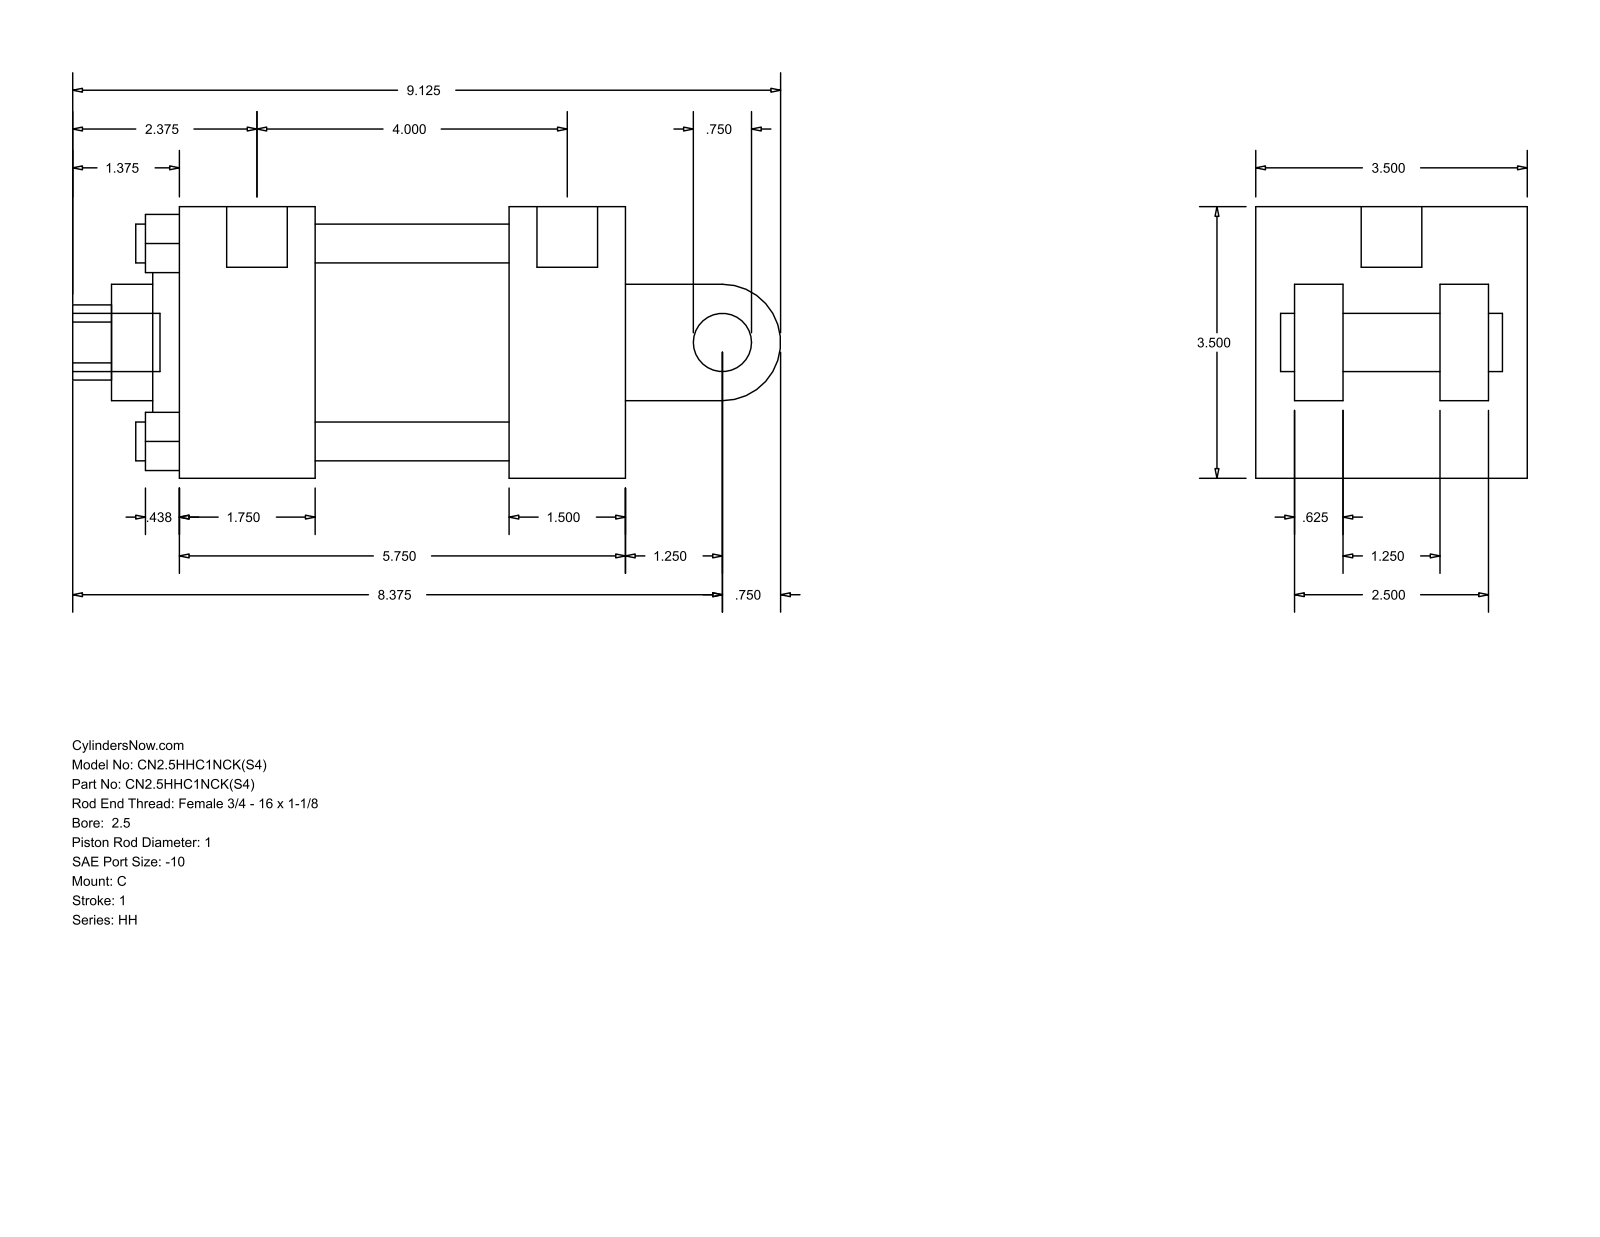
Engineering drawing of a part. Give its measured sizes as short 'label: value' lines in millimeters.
name: HH_C__0250_1
written by: GSSL Pune (CONFIG_CONTROL_DESIGN)
unit: mm
bodies: 0 solids, 101 faces (71 planar, 30 cylindrical, 0 other)
size: 231.78 × 88.9 × 88.9
holes: 4× ⌀12.7, 2× ⌀5.56, 1× ⌀19.84, 1× ⌀25.4, 1× ⌀38.1, 1× ⌀60.33, 1× ⌀73.03
bosses: 2× ⌀19.05, 2× ⌀5.56, 1× ⌀19.84
rounds: 1× R12.29, 1× R19.05
face distances: 88.9, 63.5, 146.05, 15.87, 107.96, 38.09, 44.46, 101.59, 12.7, 28.57
hole spacings: 45.79, 64.76, 91.58, 1.58
